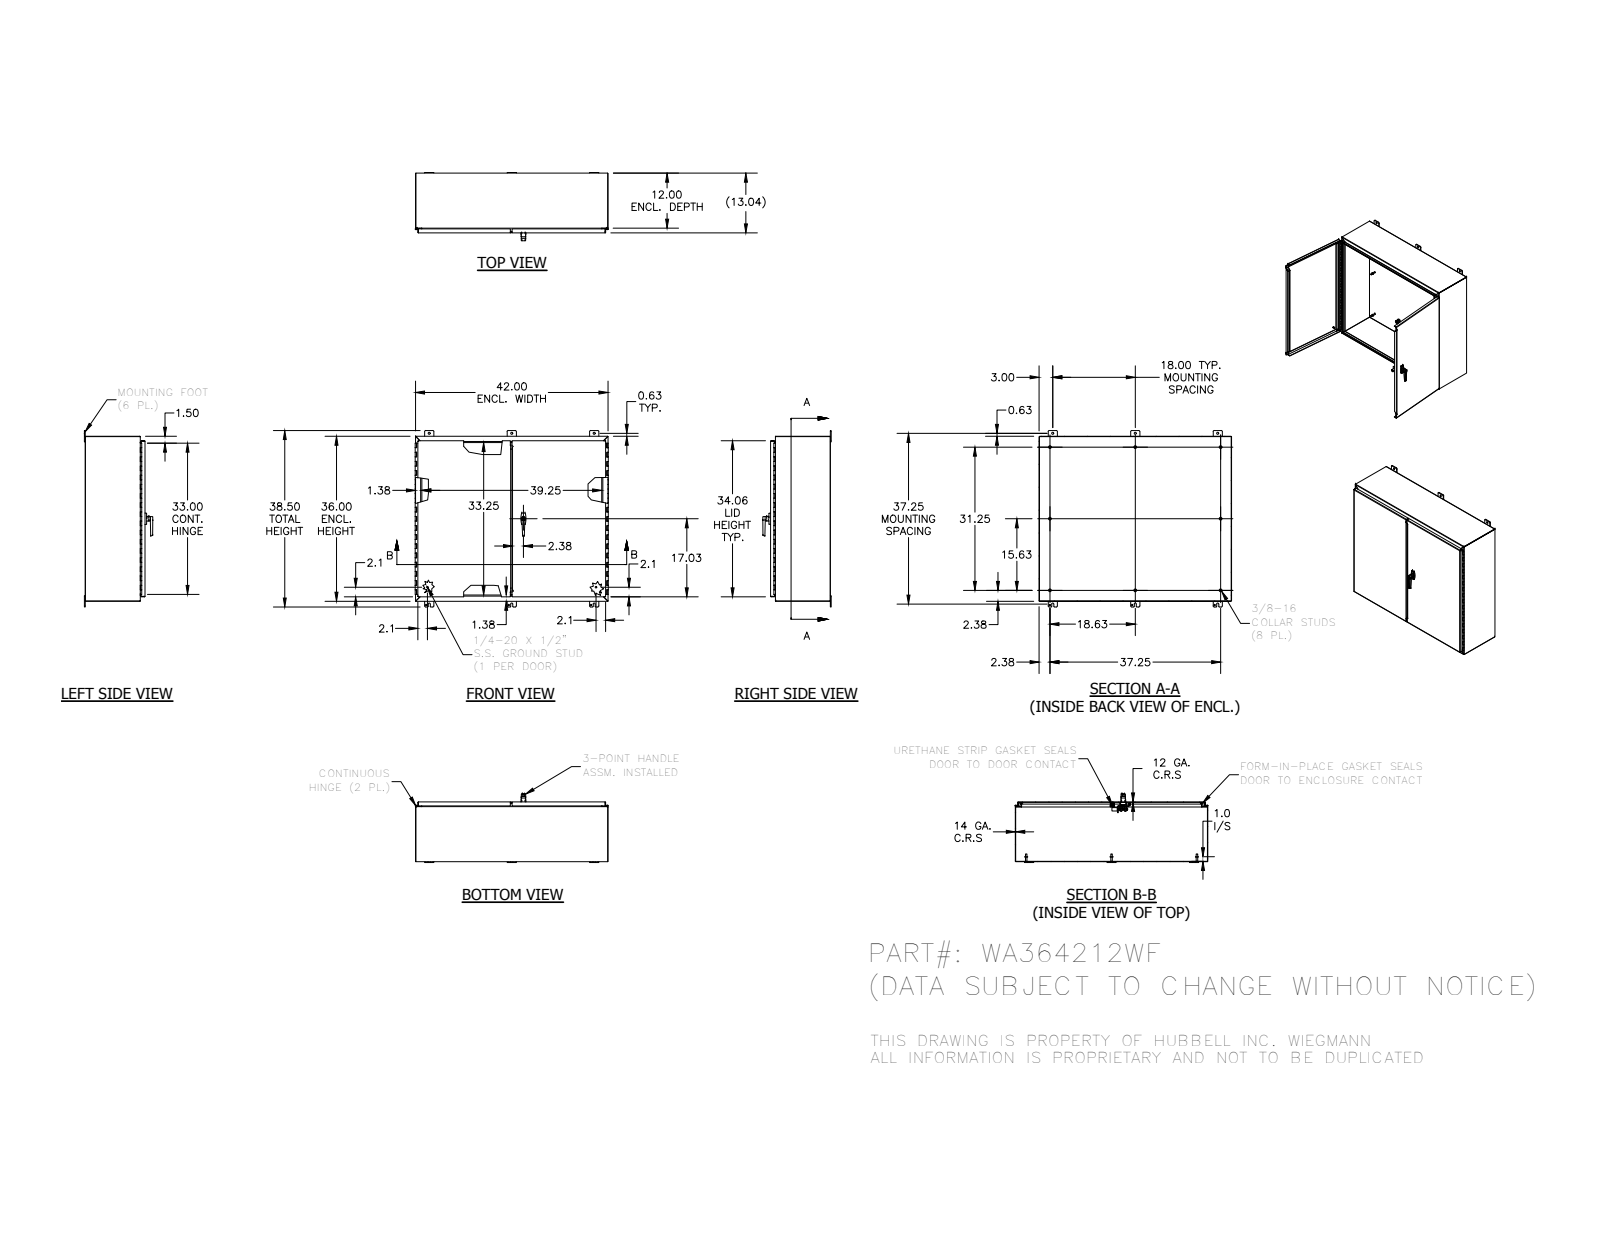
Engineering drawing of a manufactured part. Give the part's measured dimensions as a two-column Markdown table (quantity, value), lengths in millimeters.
| quantity | value |
| --- | --- |
| part name | WA364212WF; WA364212WFLRS; 34840; WA364212WFBTB (+8 more) |
| STEP written by | Autodesk Inventor 2012 (AUTOMOTIVE_DESIGN) |
| units | millimeters |
| bodies | 62 solids, 2660 faces (1474 planar, 694 cylindrical, 492 other) |
| overall size | 1070.6 × 977.9 × 378.9 |
| volume | 8 076 000 mm³ |
| surface area | 7 537 000 mm² |
| round holes (diameter × count) | 7 × 8, 2.1 × 6, 8 × 6, 11.1 × 6, 5.1 × 4, 3.2 × 2, 4 × 2, 6.1 × 2, 6.4 × 2, 6.4 × 2, 10.2 × 2, 10.3 × 2 |
| round bosses / shafts (diameter × count) | 15.9 × 8, 8.4 × 8, 4 × 7, 6.4 × 4, 2.9 × 4, 25.4 × 2, 14.3 × 2, 13.4 × 2 |
| partial cylindrical surfaces (radius × count) | 0.8 × 28, 6.4 × 24, 0.2 × 22, 0.4 × 22, 2.7 × 17, 0.3 × 16, 1.3 × 14, 3.2 × 12 |
| main face-to-face distances | 1.9, 2.4, 328.7, 326.8, 331.1, 329.2, 912.5, 1064.9, 910.6, 914.4 |
| hole center spacings | 457.2, 914.4, 1022.3, 7.4, 5.1, 40.5, 441.2, 476 |
